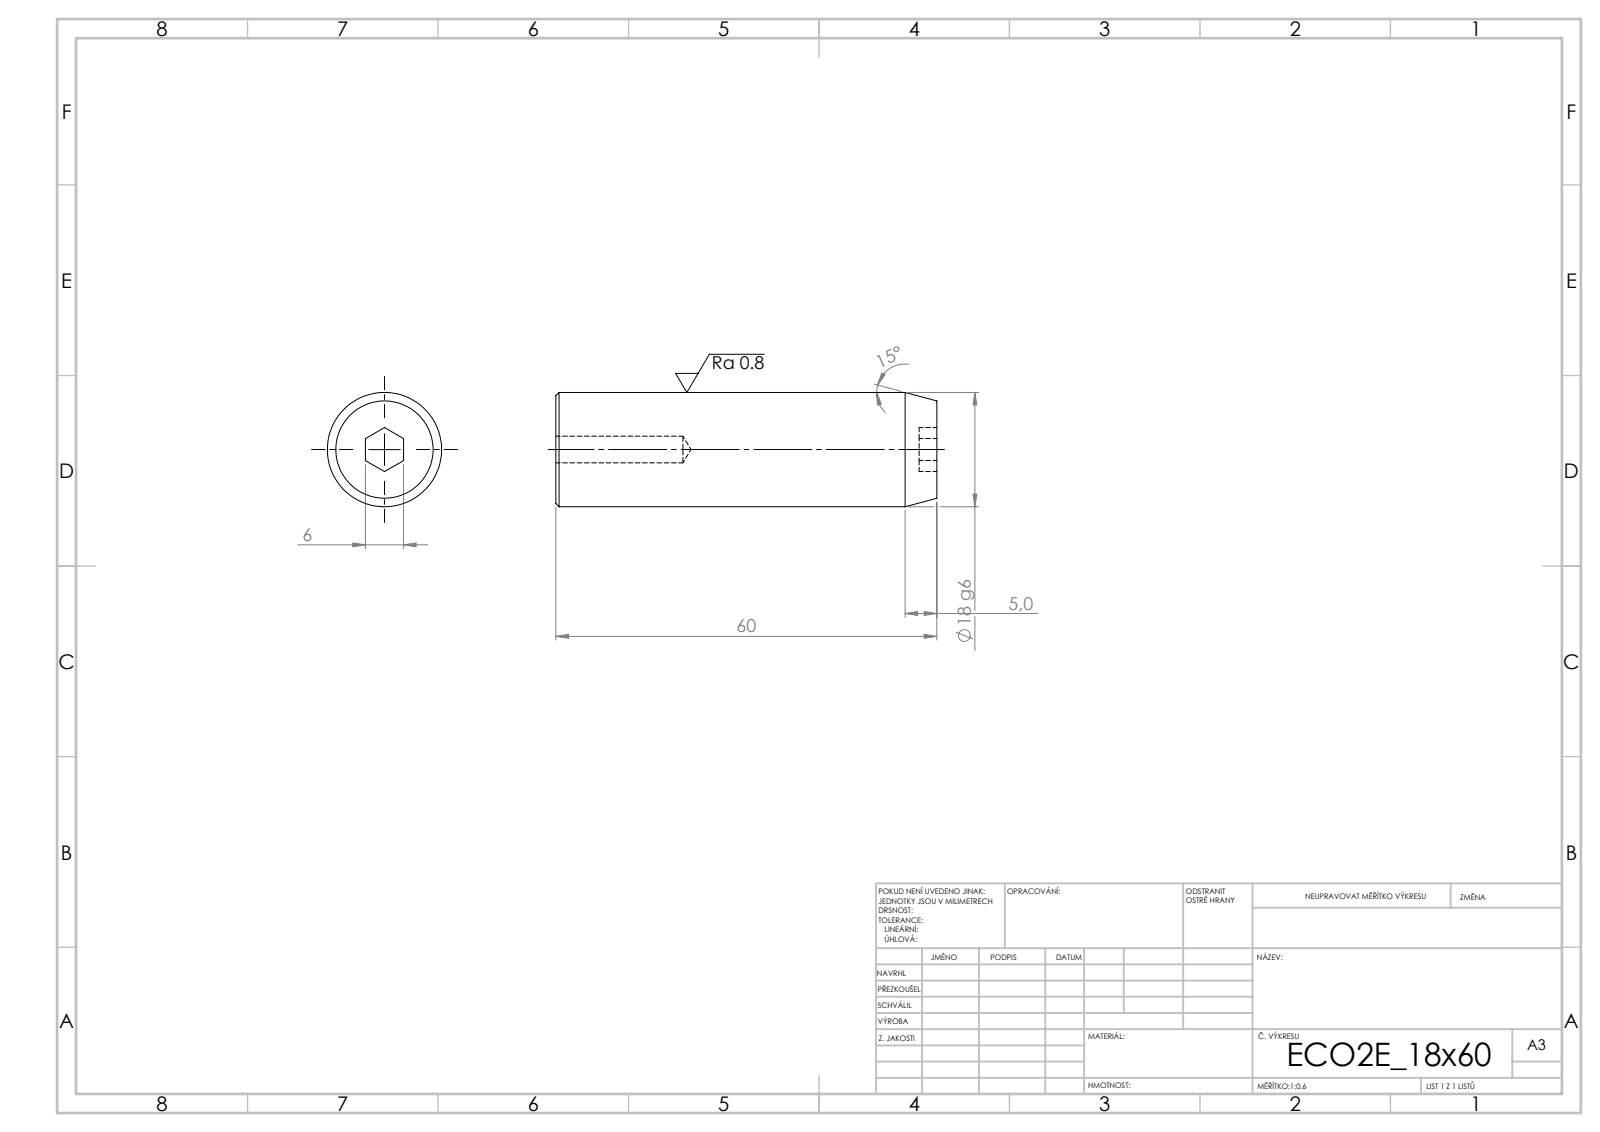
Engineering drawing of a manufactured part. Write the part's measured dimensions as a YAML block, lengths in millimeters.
step_written_by: "SolidWorks 2019 (CONFIG_CONTROL_DESIGN)"
units: millimeters
bodies: {solids: 1, faces: 19, planar: 9, cylindrical: 4, other: 6}
overall_size: [60, 18, 18]
volume: 14711
surface_area: 4127
round_holes:
  - {diameter: 4.2, count: 1}
round_bosses_or_shafts:
  - {diameter: 18, count: 1}
face_to_face_distances: [60, 2.8, 57.2, 6]
